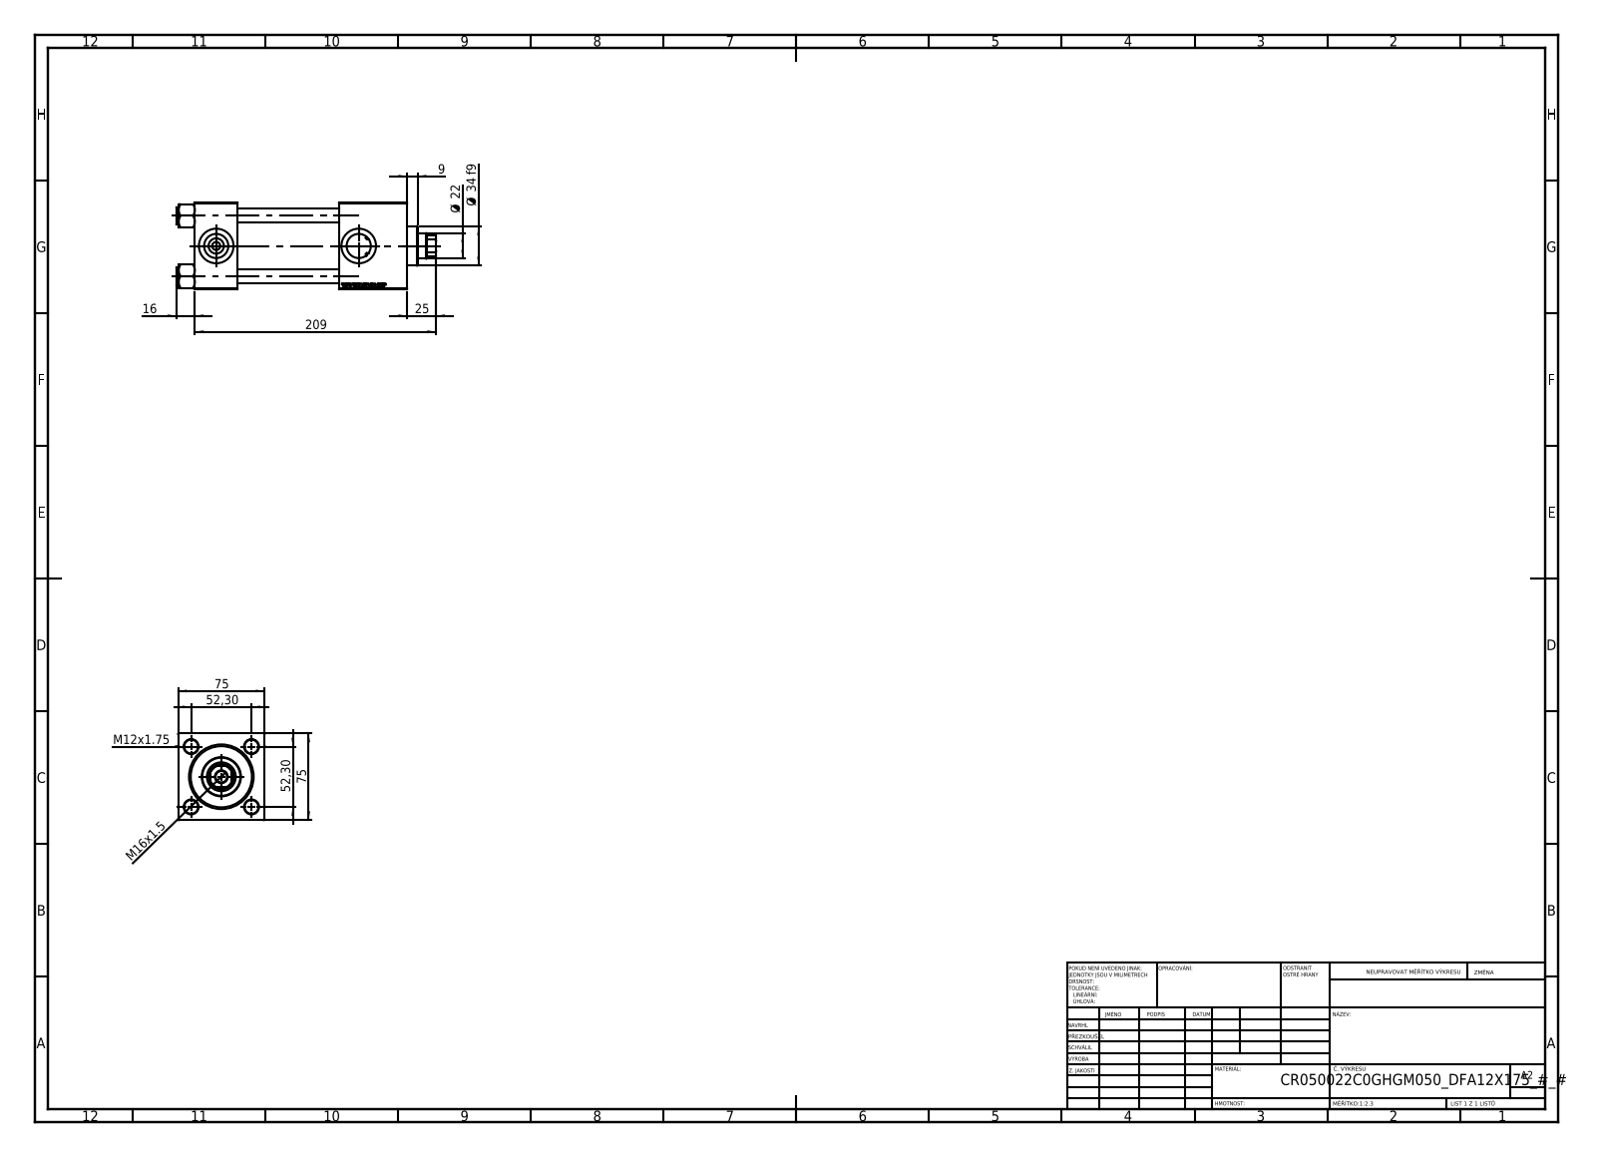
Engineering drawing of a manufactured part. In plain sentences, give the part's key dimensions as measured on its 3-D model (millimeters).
The part is named "V215CR_C_TYCINKA; NUT_M5_C; V215CR_C_Body; V215CR_VCP_C (+2 more)". Its 3-D file was written by "SolidWorks 2019 (CONFIG_CONTROL_DESIGN)". It is 12 solids with 1181 faces: 538 planar, 95 cylindrical and 548 other. Overall it measures 225 by 75.54 by 75 millimeters. Its volume is 706 737 cubic millimeters and its surface area 168 297 square millimeters. Round holes: 4 of diameter 12, 2 of diameter 7, 2 of diameter 20.96, 2 of diameter 30, 1 of diameter 10.5, 1 of diameter 22, 1 of diameter 25, 1 of diameter 41, 1 of diameter 50, 1 of diameter 53. Round bosses or shafts: 4 of diameter 15, 1 of diameter 56, 1 of diameter 34, 1 of diameter 28, 1 of diameter 24, 1 of diameter 12, 1 of diameter 10. Partial cylindrical surfaces (rounded edges, fillets, slot ends): 1 of radius 9.75, 1 of radius 10.5. The main face-to-face distances are 75, 37, 184, 147, 125, 88, 59, 155.3, 118.3, 30.3. The hole center spacings are 36.98, 52.3, 73.96, 123.5.
